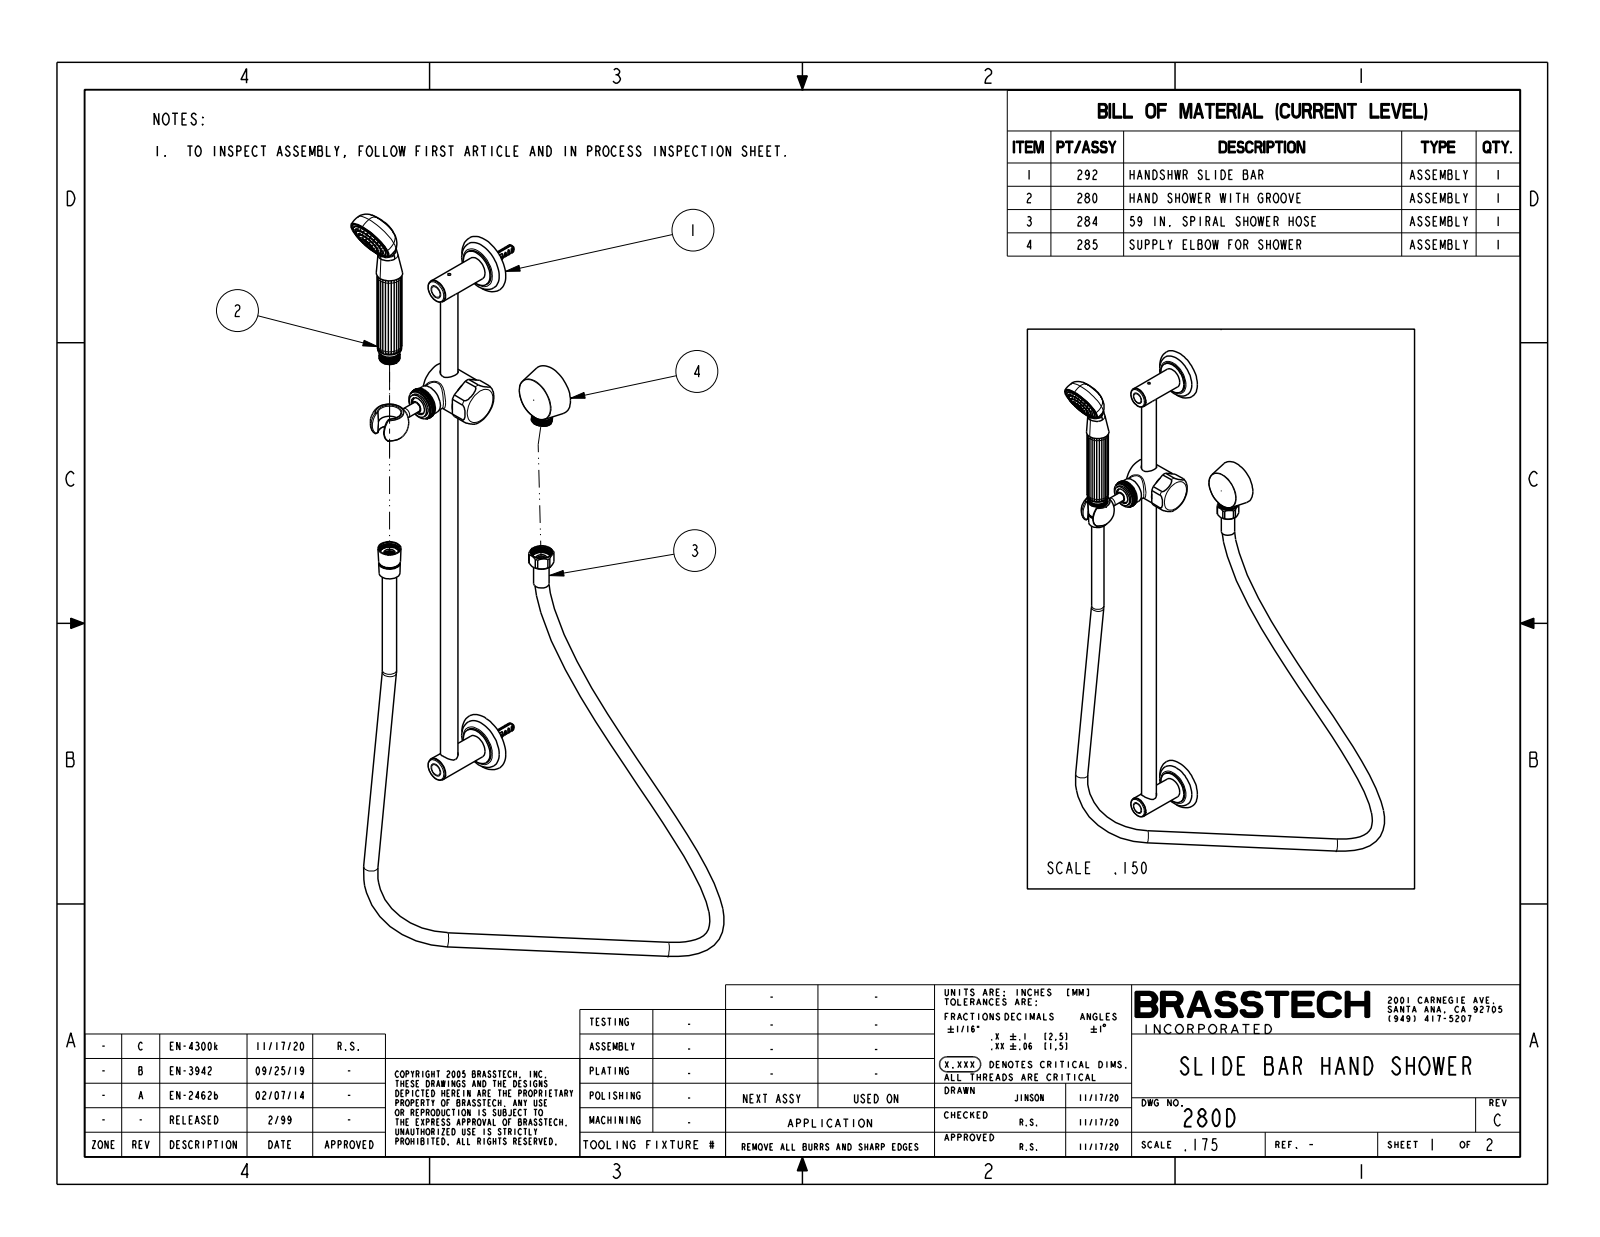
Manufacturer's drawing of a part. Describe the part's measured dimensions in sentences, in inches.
The part is named "280D". Its 3-D file was written by "CREO PARAMETRIC BY PTC INC, 2018400 (CONFIG_CONTROL_DESIGN)". It is 1 solid with 653 faces: 267 planar, 130 cylindrical and 256 other. Overall it measures 27.555 by 11.919 by 9.495 inches. Its volume is 42.42 cubic inches and its surface area 241.6 square inches. Round holes: 27 of diameter 0.046, 1 of diameter 0.675, 1 of diameter 0.727, 1 of diameter 1.05. Round bosses or shafts: 3 of diameter 0.56, 2 of diameter 1.482, 2 of diameter 0.938, 1 of diameter 1.823, 1 of diameter 1.65, 1 of diameter 1.63, 1 of diameter 1.26, 1 of diameter 1.16. Partial cylindrical surfaces (rounded edges, fillets, slot ends): 4 of radius 0.03, 1 of radius 0.406, 1 of radius 0.409, 1 of radius 0.494, 1 of radius 0.875. The main face-to-face distances are 0.437, 1.6, 2.624, 2.187, 1.625, 2.275, 0.65, 0.375, 0.062, 2.249. The hole center spacings are 0.367, 0.863, 0.185, 0.185, 0.187, 0.542, 1.002, 0.708.
